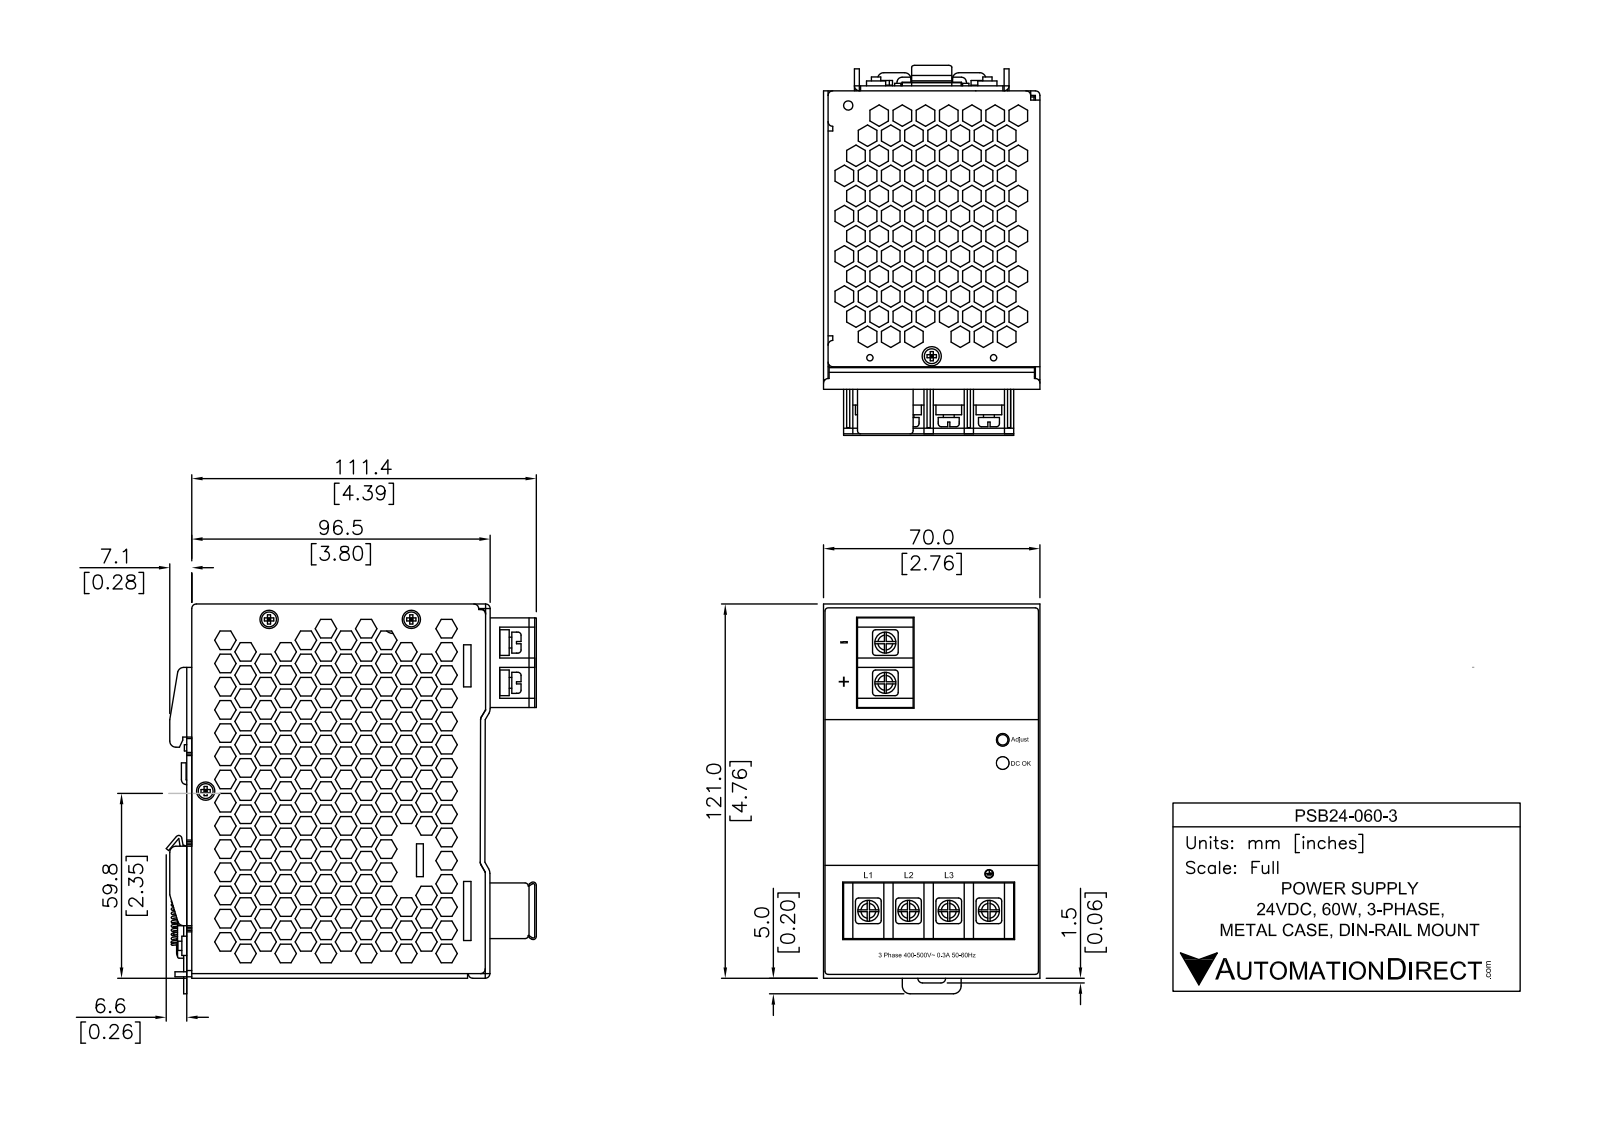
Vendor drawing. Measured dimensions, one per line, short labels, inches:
name: PSB24-060-3.
written by: SolidWorks 2011 (CONFIG_CONTROL_DESIGN)
unit: in
bodies: 2 solids, 3866 faces (3698 planar, 97 cylindrical, 71 other)
size: 4.946 × 4.572 × 2.76
volume: 44.82 in³; area: 243.3 in²
holes: 2× ⌀0.145
bosses: 4× ⌀0.205, 4× ⌀0.125, 2× ⌀0.23
rounds: 21× R0.06, 12× R0.03, 8× R0.05, 3× R0.04, 2× R0.04, 2× R0.075, 2× R0.13, 1× R0.01
face distances: 0.148, 2.608, 0.07, 0.078, 2.678, 2.53, 2.46, 0.06, 0.075, 3.583
hole spacings: 0.3
